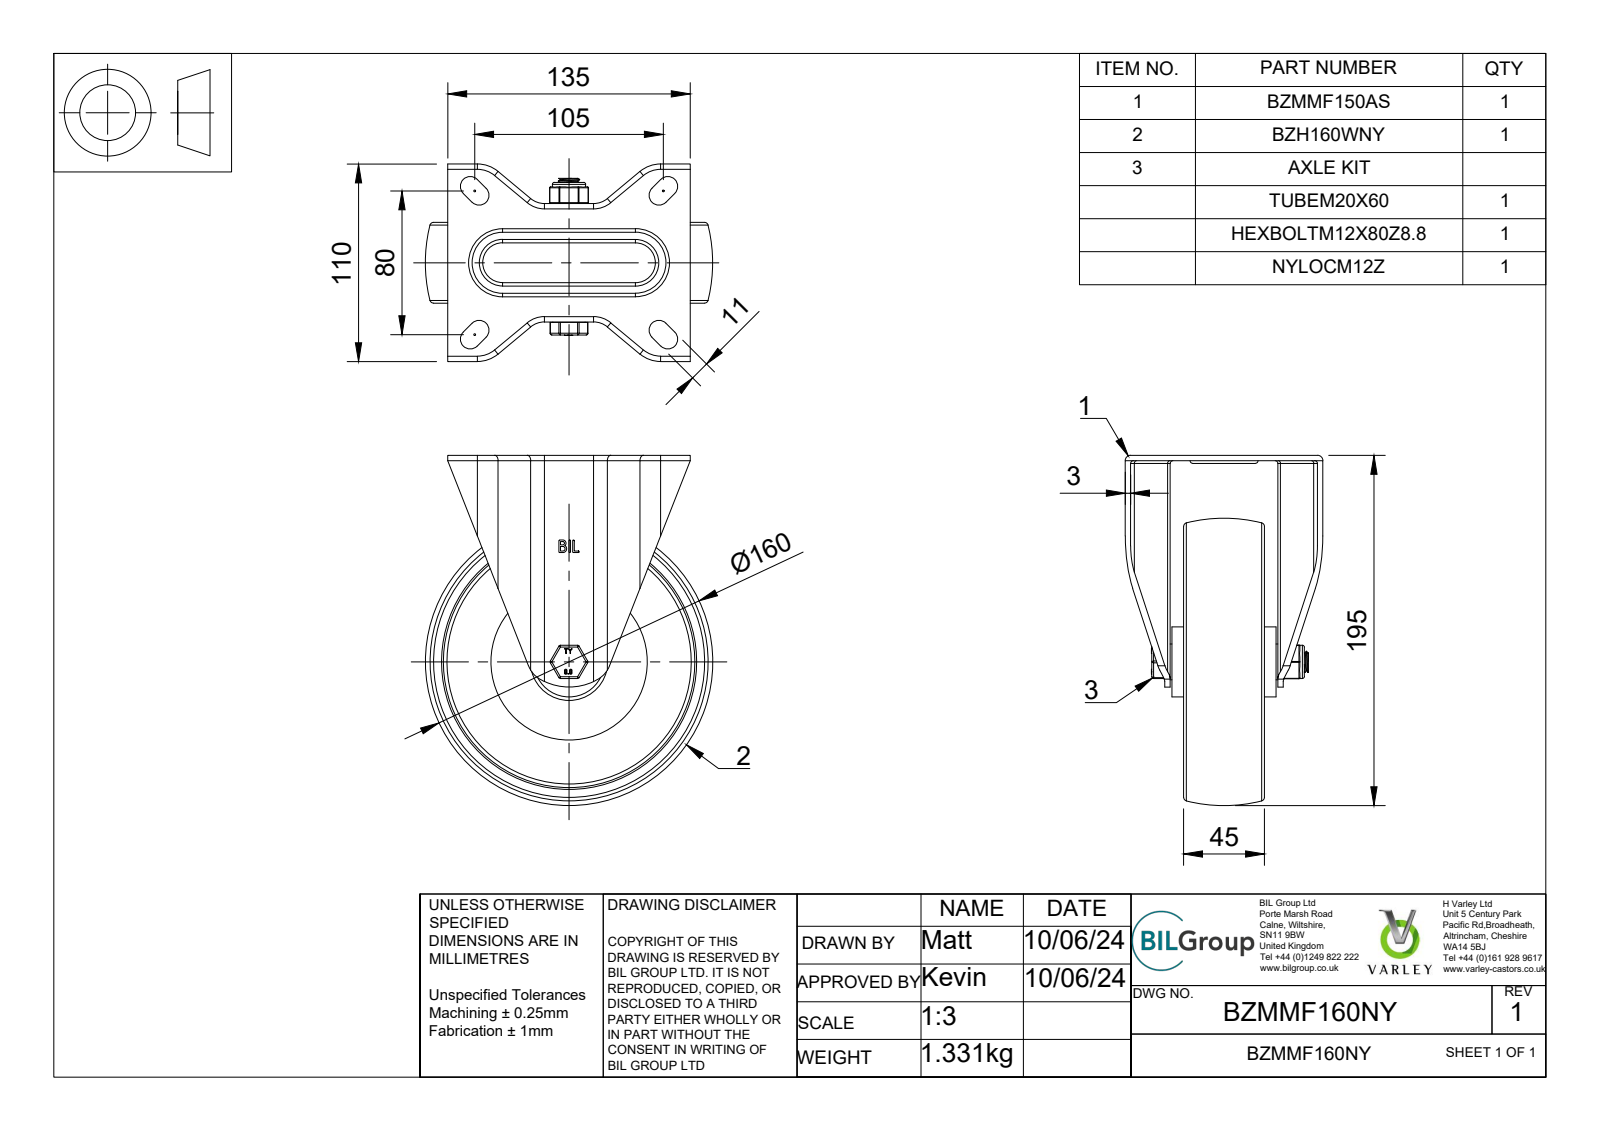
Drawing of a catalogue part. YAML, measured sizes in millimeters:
part_name: "BZMMF160NY v3; BZMMF150AS v1; BZMMF150AS; ZINC PLATED, PRESSED STEEL BRACKET (+8 more)"
step_written_by: "Autodesk Translation Framework v13.14.0.145 (AUTOMOTIVE_DESIGN)"
units: millimeters
bodies: {solids: 6, faces: 378, planar: 128, cylindrical: 144, other: 106}
overall_size: [195, 160, 110]
volume: 485403
surface_area: 170569
round_holes:
  - {diameter: 12, count: 1}
  - {diameter: 12.25, count: 1}
  - {diameter: 12.5, count: 1}
  - {diameter: 14, count: 1}
  - {diameter: 20.5, count: 1}
  - {diameter: 140, count: 1}
round_bosses_or_shafts:
  - {diameter: 39, count: 1}
  - {diameter: 19.9, count: 1}
  - {diameter: 18.5, count: 1}
  - {diameter: 18, count: 1}
  - {diameter: 11.83, count: 1}
  - {diameter: 9.84, count: 1}
partial_cylinders:
  - {radius: 0.5, count: 18}
  - {radius: 1, count: 12}
  - {radius: 1.5, count: 12}
  - {radius: 3, count: 8}
  - {radius: 5.5, count: 8}
  - {radius: 2, count: 4}
  - {radius: 6, count: 4}
  - {radius: 9, count: 4}
face_to_face_distances: [3, 24.74, 7, 29.5, 26.5, 33.5, 36.5, 63, 19, 55.5]
